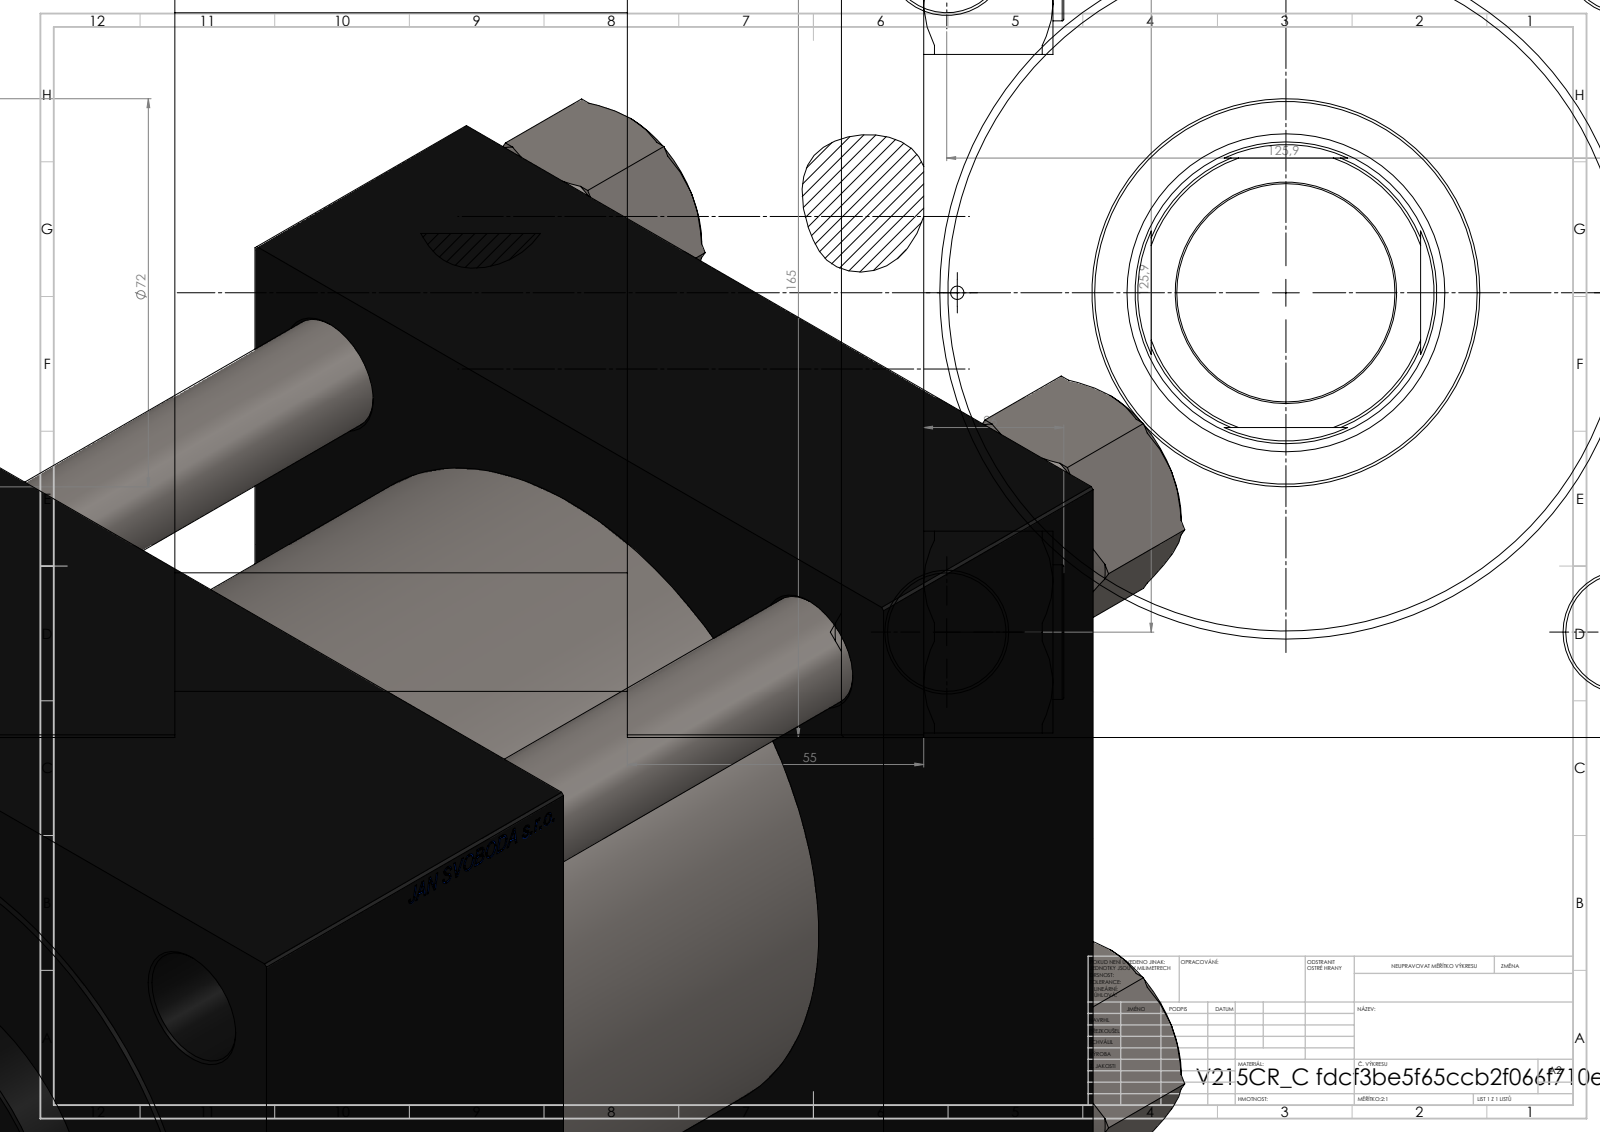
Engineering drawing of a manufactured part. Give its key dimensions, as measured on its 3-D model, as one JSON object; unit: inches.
{"part_name": "V215_VC_A; V215CR_C_TYCINKA; V215CR_C_Body; NUT_M5_C (+1 more)", "step_written_by": "SolidWorks 2019 (CONFIG_CONTROL_DESIGN)", "units": "inches", "bodies": {"solids": 11, "faces": 1203, "planar": 576, "cylindrical": 91, "other": 536}, "overall_size": [10.945, 6.659, 6.496], "volume_in3": 274.2, "surface_area_in2": 781, "round_holes": [[0.866, 4], [0.098, 2], [0.276, 2], [1.269, 2], [1.772, 2], [1.594, 1], [2.205, 1], [2.323, 1], [3.78, 1], [4.921, 1], [4.941, 1]], "round_bosses_or_shafts": [[0.984, 4], [5.157, 1], [2.835, 1]], "partial_cylinders_radius": [[1.063, 1]], "face_to_face_distances": [6.496, 2.165, 6.378, 8.543, 5.472, 3.307, 3.071, 7.413, 5.248, 1.941], "hole_center_spacings": [2.48, 3.505, 4.957, 5.473, 2.402, 7.01, 4.803, 5.453]}
